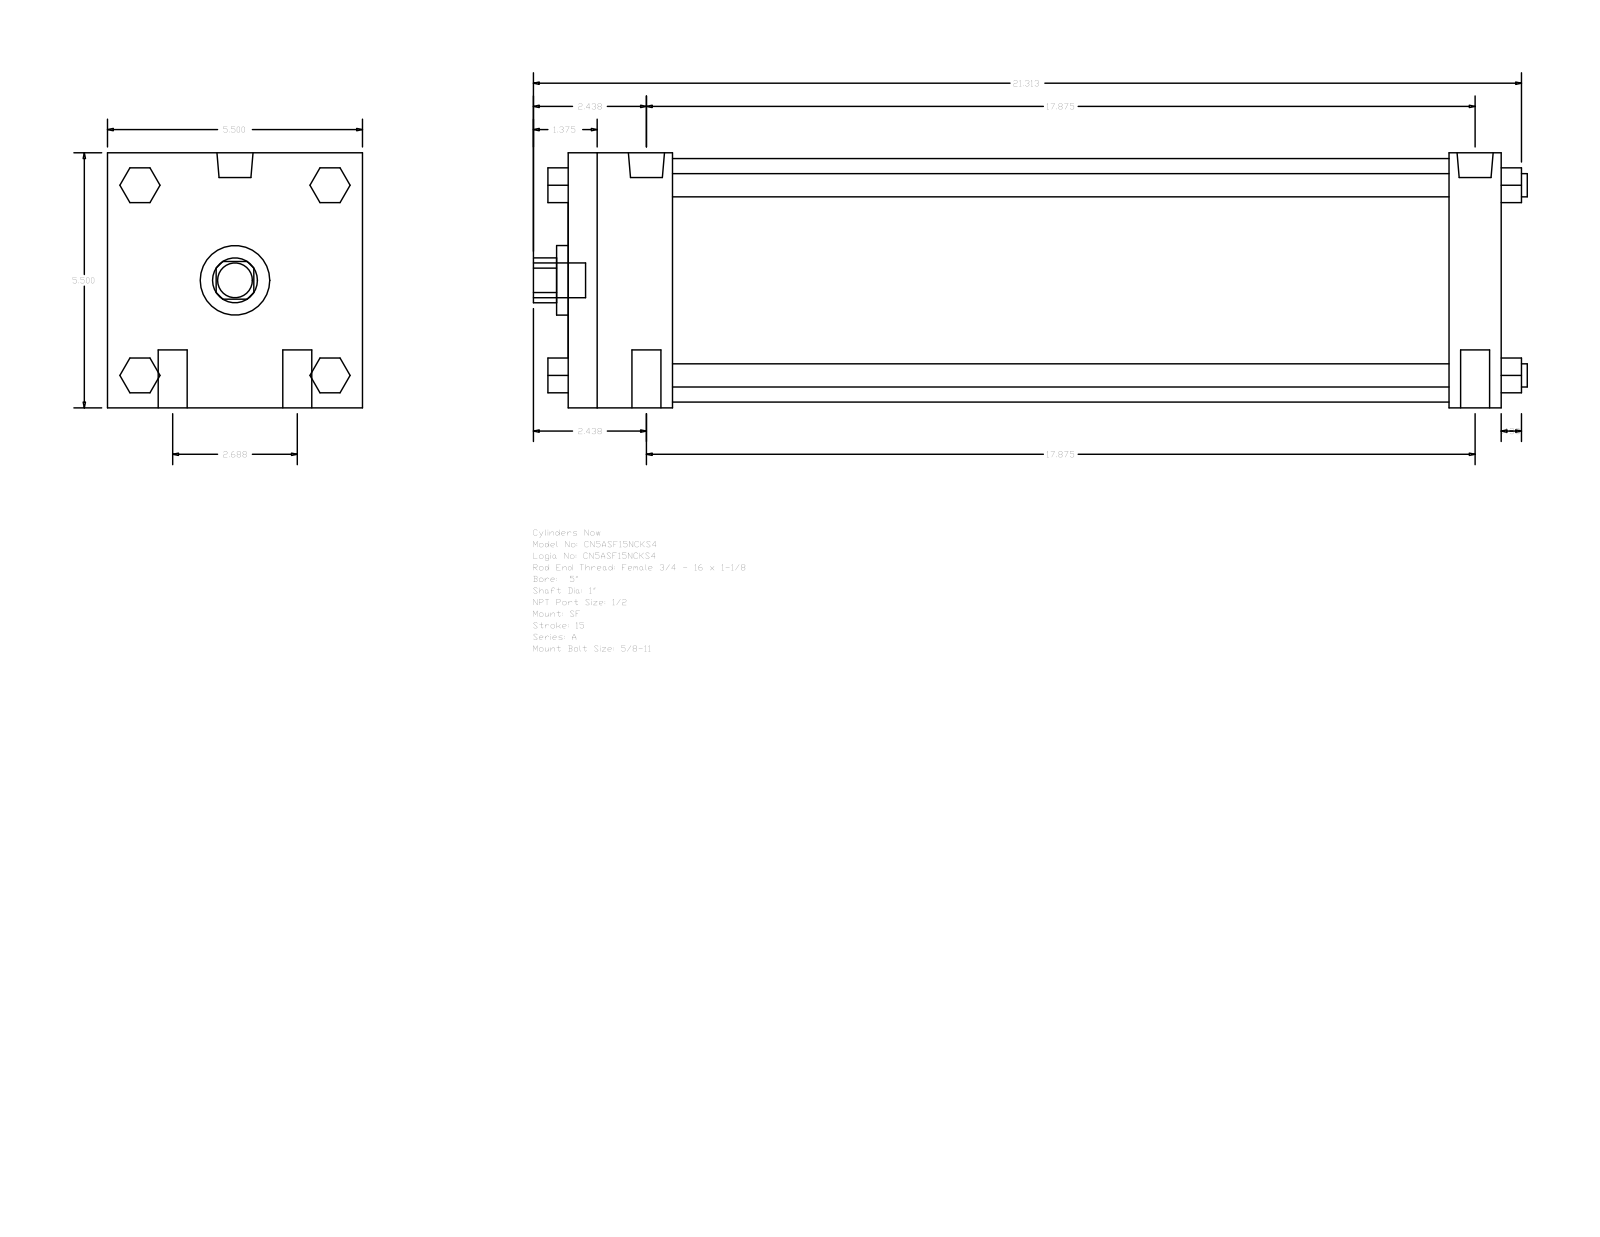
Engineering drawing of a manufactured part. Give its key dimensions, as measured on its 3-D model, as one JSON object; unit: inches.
{"part_name": "A_SF__0500_1", "step_written_by": "GSSL Pune (CONFIG_CONTROL_DESIGN)", "units": "inches", "bodies": {"solids": 0, "faces": 124, "planar": 94, "cylindrical": 30, "other": 0}, "overall_size": [21.437, 5.5, 5.5], "round_holes": [[1, 1], [1.5, 1], [5.25, 1]], "round_bosses_or_shafts": [[0.625, 4], [0.5, 4], [0.778, 2], [0.344, 2], [0.75, 1]], "partial_cylinders_radius": [[0.484, 1]], "face_to_face_distances": [5.5, 20.125, 2.25, 19, 16.75, 17.875, 1.125, 0.75, 2.05, 3.55]}
